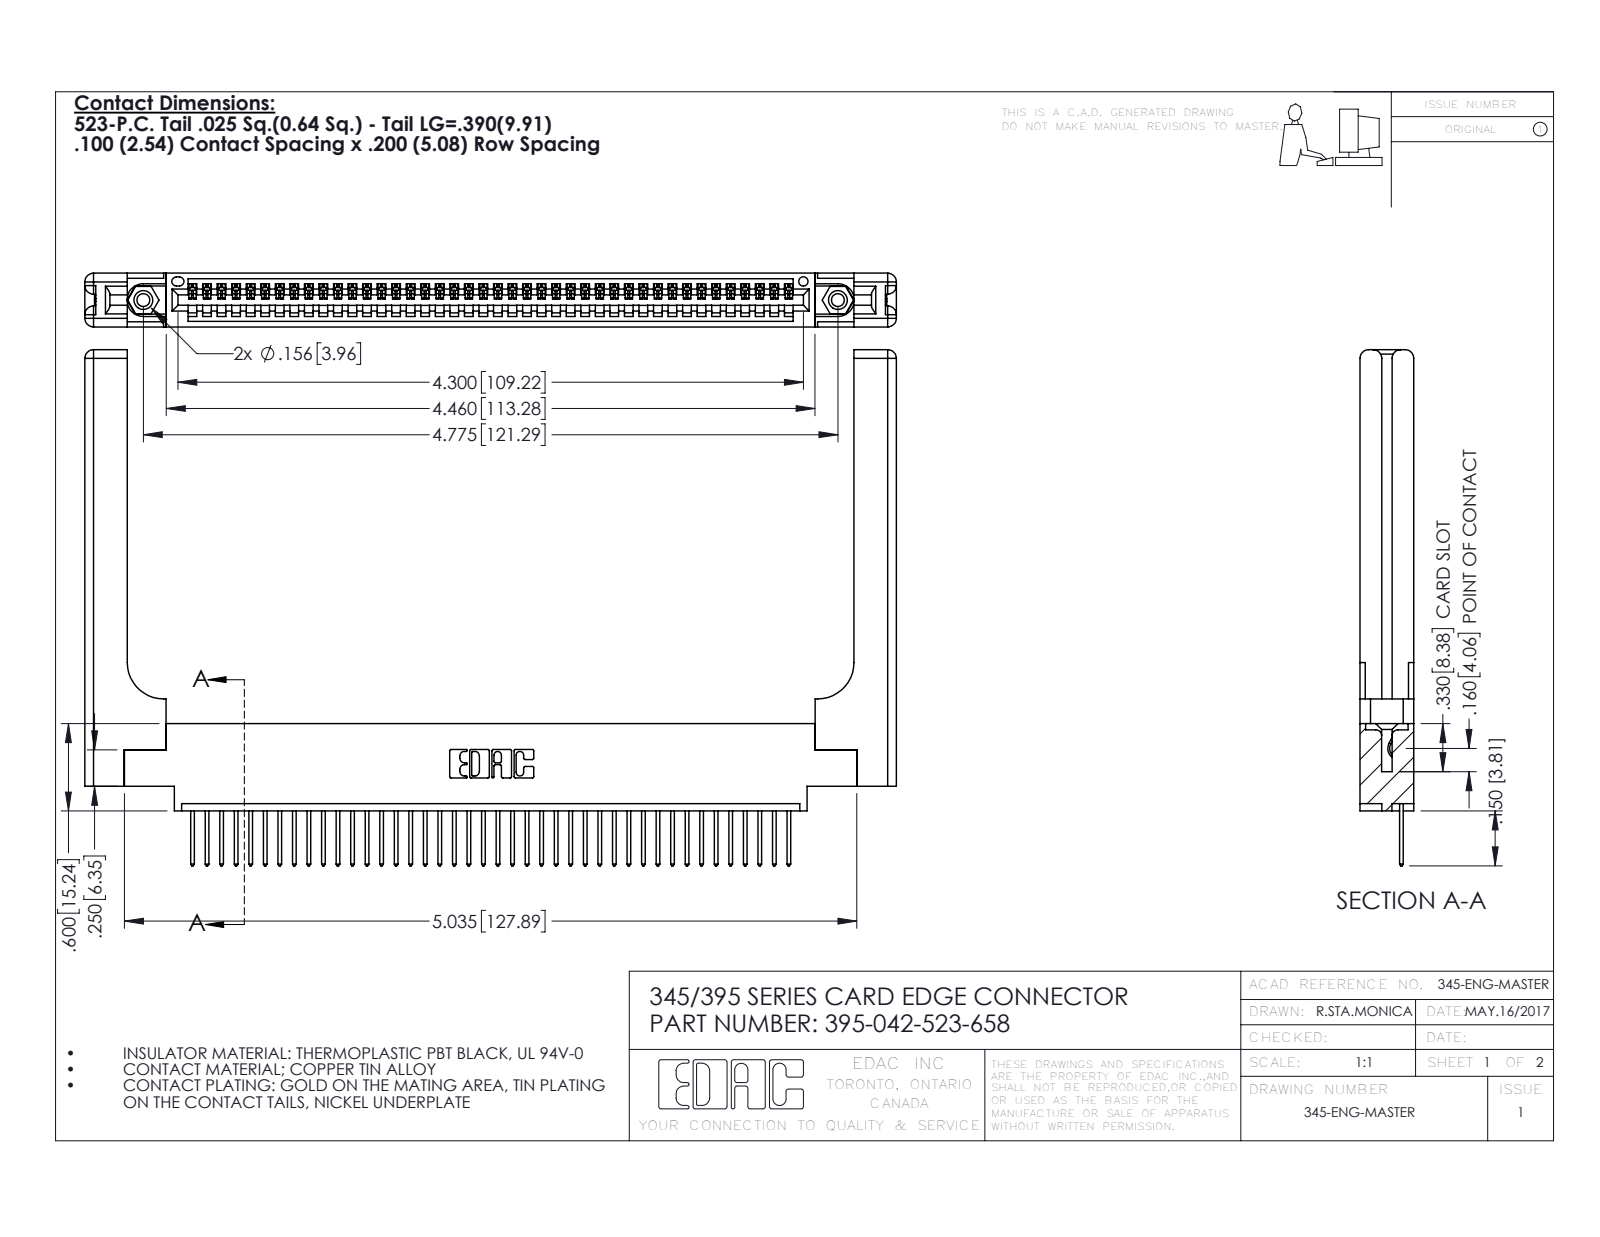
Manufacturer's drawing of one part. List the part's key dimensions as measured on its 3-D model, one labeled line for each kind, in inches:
Part name (STEP PRODUCT): 395-042-523-658; 345-250-001_345-250-001-102; 345 Part_0.170 Offset - 0.156 Dia-TH; 345-220-058_345-220-058 (+1 more)
STEP written by: SolidWorks 2016 (CONFIG_CONTROL_DESIGN)
Units: inches
Bodies: 47 solids, 2822 faces (1912 planar, 850 cylindrical, 60 other)
Overall size (bounding box): 5.579 × 3.547 × 0.37
Volume: 1.332 in³ · Surface area: 35.95 in²
Round holes (diameter × count): ⌀0.089 ×2, ⌀0.125 ×2, ⌀0.156 ×2, ⌀0.064 ×1
Round bosses / shafts (diameter × count): ⌀0.155 ×2
Partial cylindrical surfaces — rounded edges, fillets, slot ends (radius × count): R0.006 ×84, R0.01 ×84, R0.01 ×22, R0.06 ×16, R0.007 ×6, R0.031 ×6, R0.026 ×3, R0.03 ×2
Main face-to-face distances: 0.37, 0.072, 0.298, 0.098, 0.272, 0.025, 0.2, 0.148, 0.15, 0.225
Hole centre spacings: 0.27, 4.539, 4.775
